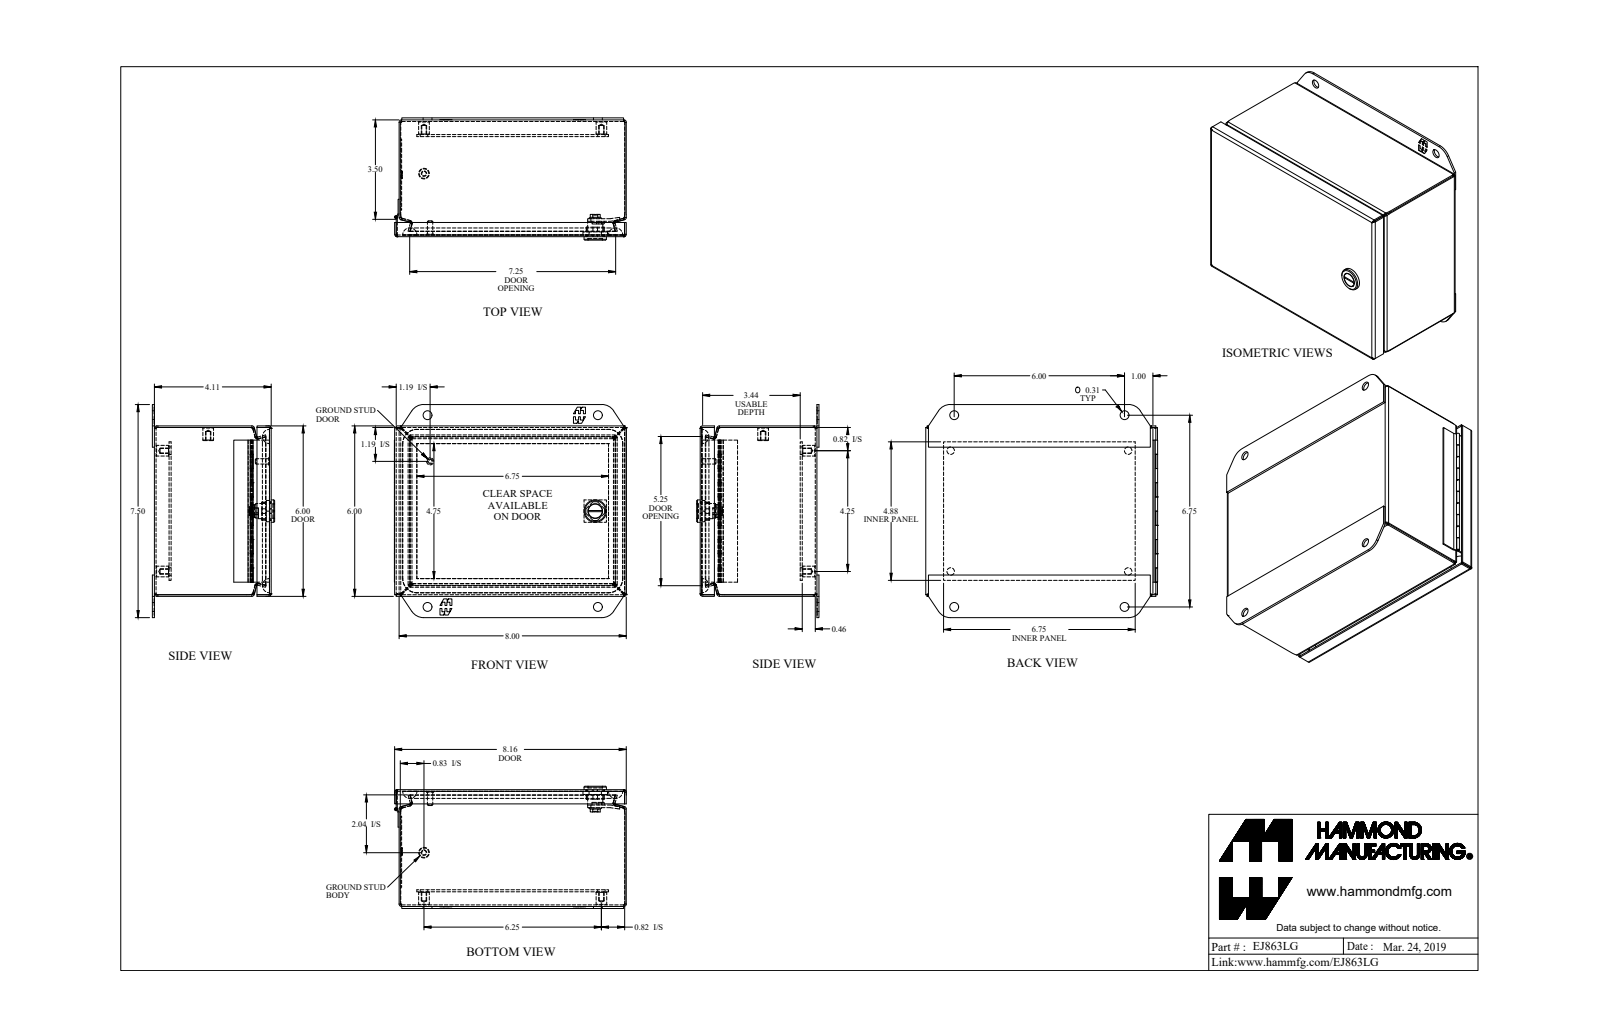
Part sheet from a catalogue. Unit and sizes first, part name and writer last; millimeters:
Units: millimetres
Overall size (bounding box): 241.3 × 156.6 × 109.3
Round holes (diameter × count): ⌀4 ×5, ⌀6.7 ×4, ⌀8 ×4, ⌀1.3 ×1, ⌀13.1 ×1
Round bosses / shafts (diameter × count): ⌀9.5 ×5, ⌀20 ×1, ⌀13.6 ×1, ⌀12.6 ×1, ⌀11 ×1, ⌀6.4 ×1, ⌀4.8 ×1, ⌀2.5 ×1
Partial cylindrical surfaces — rounded edges, fillets, slot ends (radius × count): R0.7 ×16, R2.2 ×16, R7.1 ×10, R6.4 ×4, R12.7 ×4, R12.7 ×4, R1.5 ×2, R13.7 ×2
Main face-to-face distances: 1.4, 103, 151, 1.8, 15, 104.4, 101.5, 201.8, 11.7, 13.1
Hole centre spacings: 31.9, 109.5, 190.6, 217.4, 79.6, 101.6, 108, 111.2
Volume: 317 400 mm³ · Surface area: 410 700 mm²
Bodies: 16 solids, 643 faces (361 planar, 190 cylindrical, 92 other)
Part name (STEP PRODUCT): EJ863LG_Default
STEP written by: SolidWorks 2019 (CONFIG_CONTROL_DESIGN)
